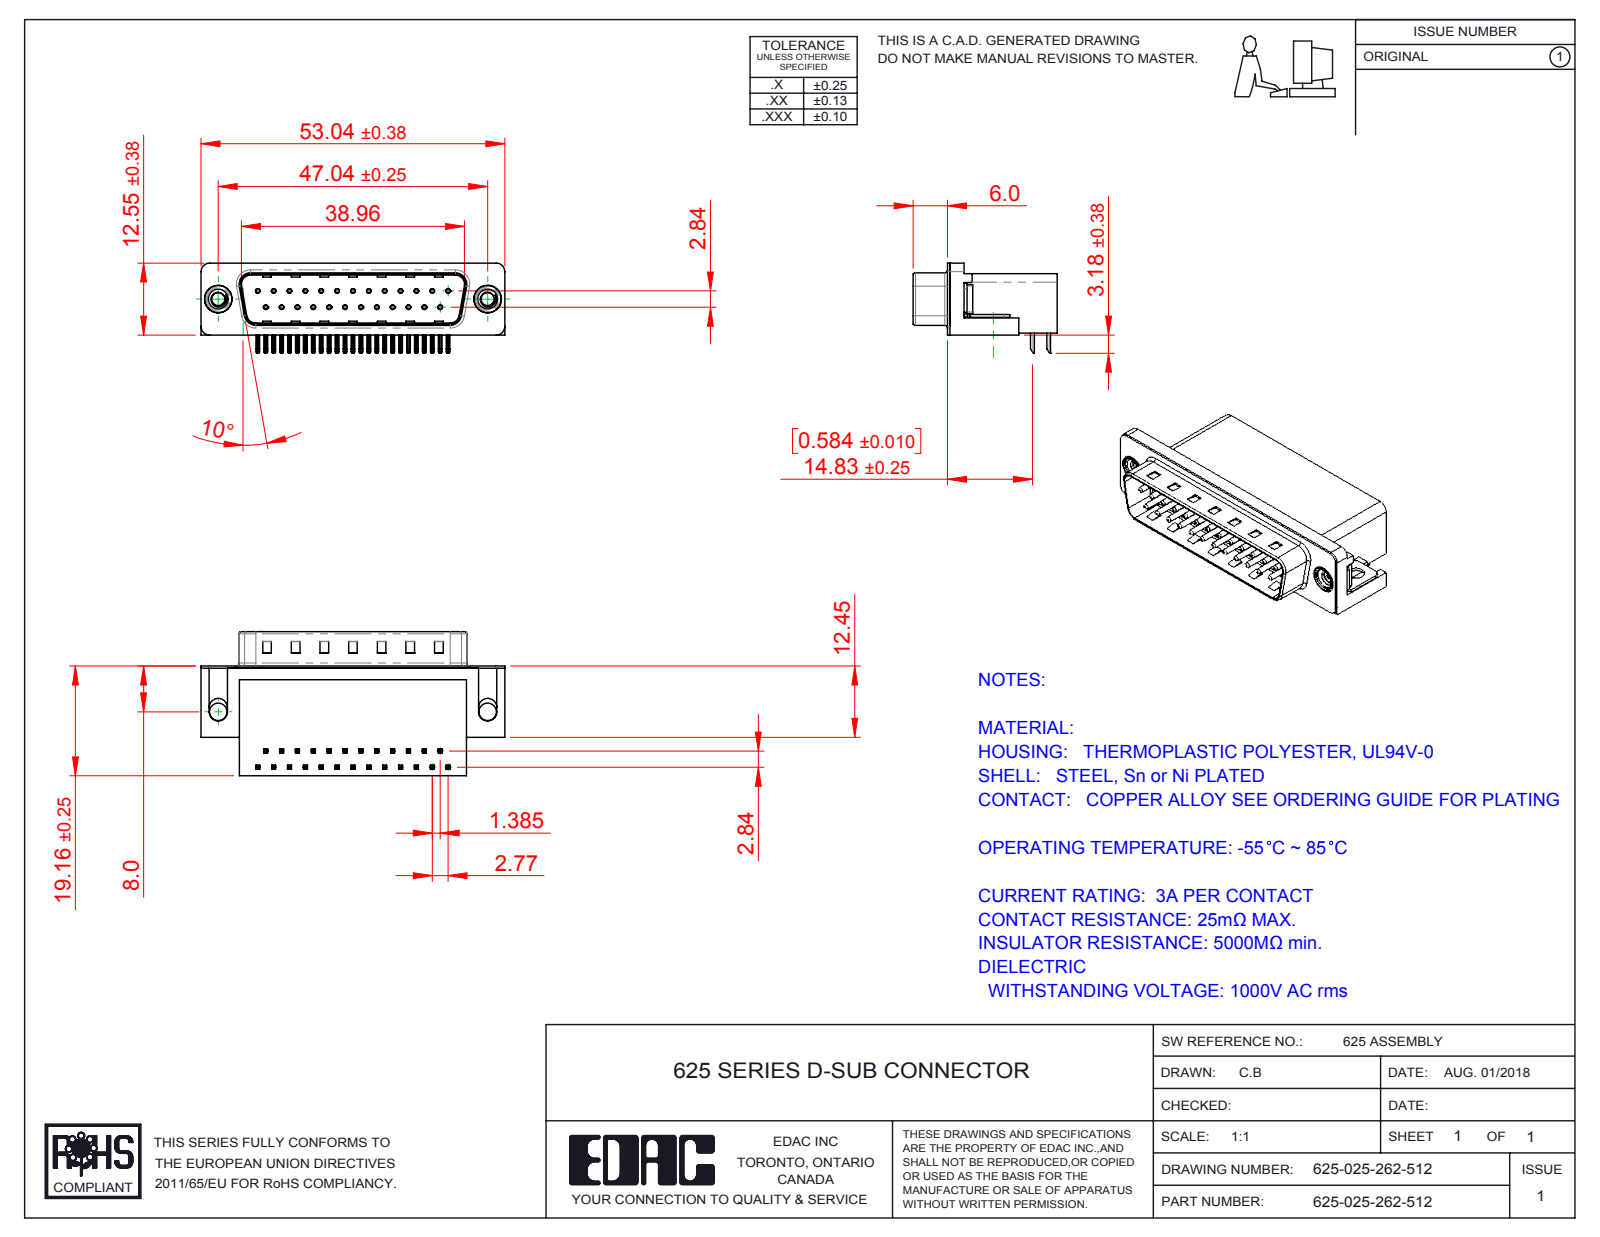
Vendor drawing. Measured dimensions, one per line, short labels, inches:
name: 625-025-262-512; 625 Contact Top; 625 Shell_25 Socket; 625 Contact Bottom (+3 more)
written by: SolidWorks 2016 (CONFIG_CONTROL_DESIGN)
unit: in
bodies: 31 solids, 2265 faces (1405 planar, 661 cylindrical, 199 other)
size: 2.088 × 0.991 × 0.619
volume: 0.559 in³; area: 13.72 in²
holes: 25× ⌀0.014, 25× ⌀0.031, 2× ⌀0.089, 2× ⌀0.12, 2× ⌀0.157, 2× ⌀0.189, 2× ⌀0.197
bosses: 25× ⌀0.03, 2× ⌀0.193, 2× ⌀0.187, 2× ⌀0.154
rounds: 108× R0.01, 50× R0.005, 16× R0.039, 9× R0.02, 8× R0.063, 7× R0.059, 4× R0.035, 4× R0.079
face distances: 0.016, 0.407, 0.739, 0.083, 0.345, 0.412, 0.428, 0.067, 0.754, 0.398
hole spacings: 0.124, 0.109, 0.436, 0.218, 0.327, 0.198, 0.545, 0.294
